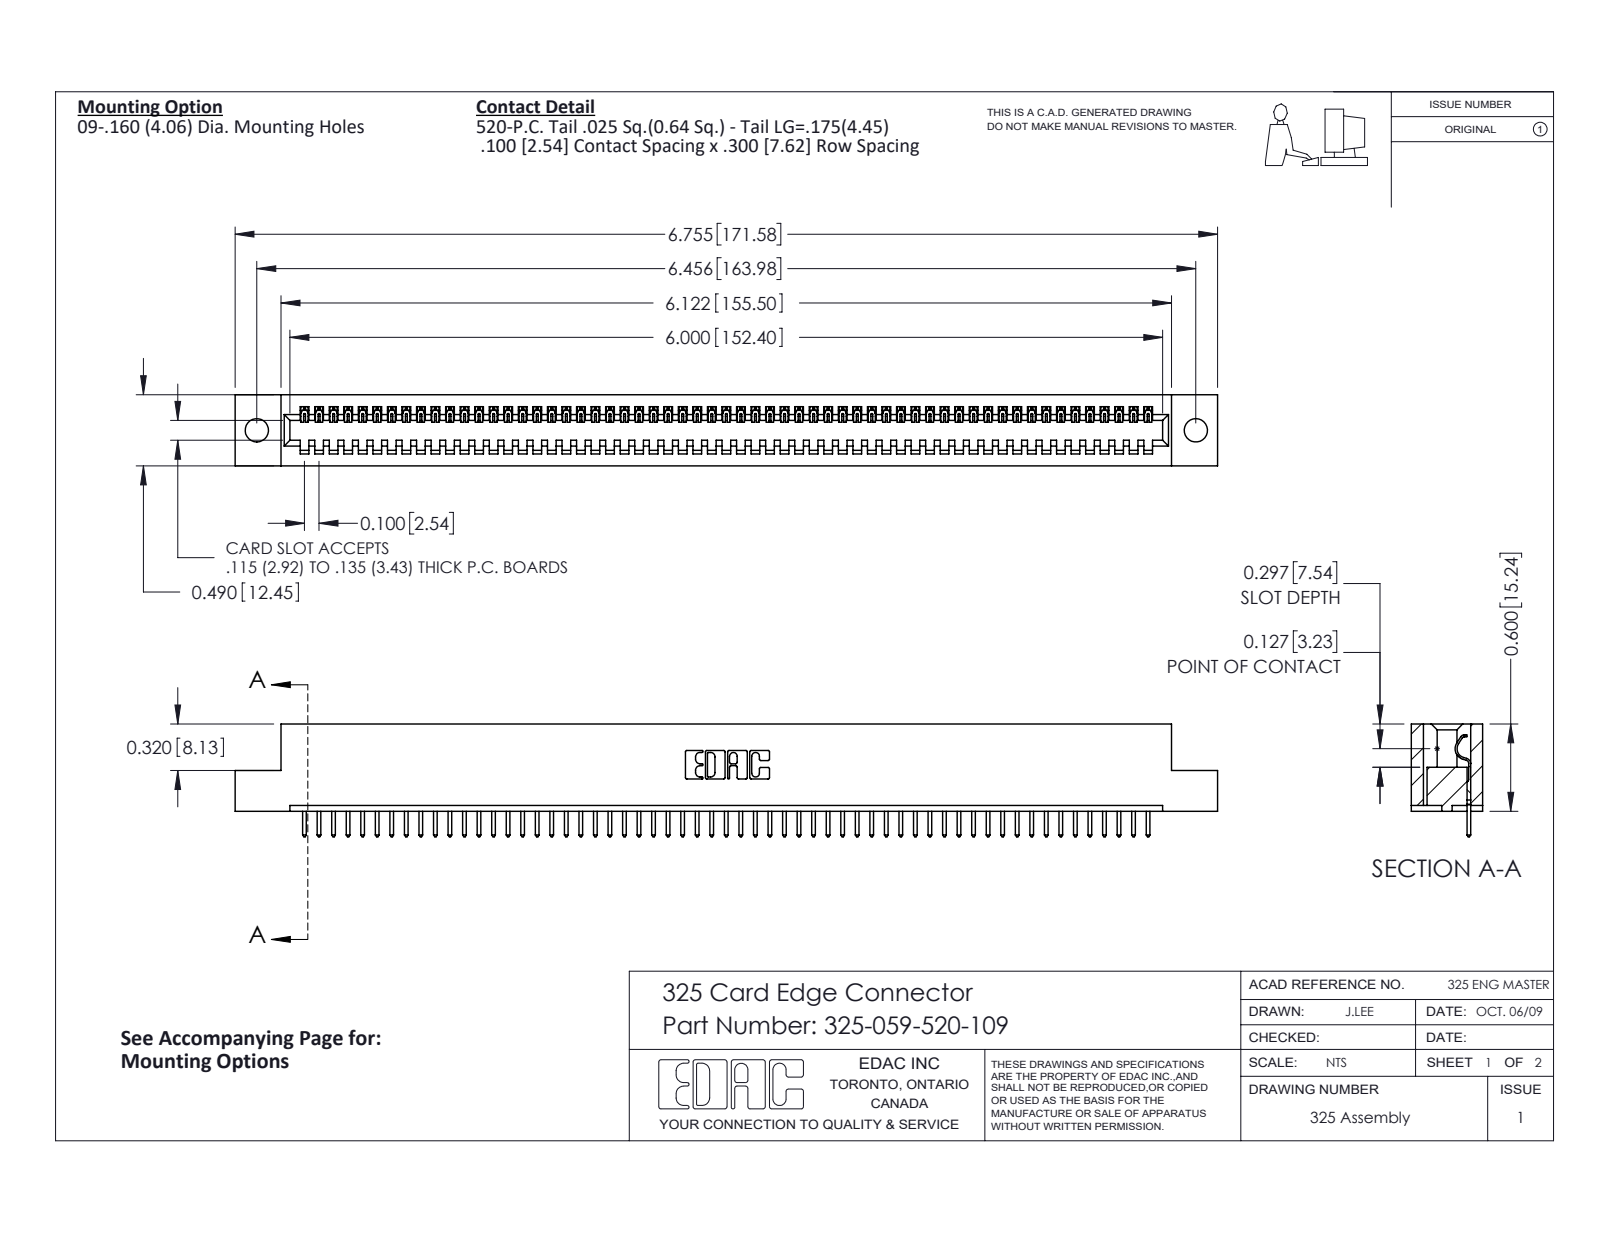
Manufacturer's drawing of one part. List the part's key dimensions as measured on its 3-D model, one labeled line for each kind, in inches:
Part name (STEP PRODUCT): 325 Part_.160 TH; 325-292-001_325-293-120; 325-059-520-109
STEP written by: SolidWorks 2016 (CONFIG_CONTROL_DESIGN)
Units: inches
Bodies: 60 solids, 3536 faces (2548 planar, 988 cylindrical, 0 other)
Overall size (bounding box): 6.755 × 0.775 × 0.49
Volume: 1.314 in³ · Surface area: 35.79 in²
Round holes (diameter × count): ⌀0.16 ×2
Partial cylindrical surfaces — rounded edges, fillets, slot ends (radius × count): R0.006 ×118, R0.01 ×118, R0.01 ×22, R0.007 ×6, R0.031 ×6, R0.026 ×3, R0.014 ×1, R0.022 ×1
Main face-to-face distances: 0.083, 0.407, 0.49, 0.3, 0.107, 0.383, 0.025, 0.325, 0.56, 0.263
Hole centre spacings: 6.456
